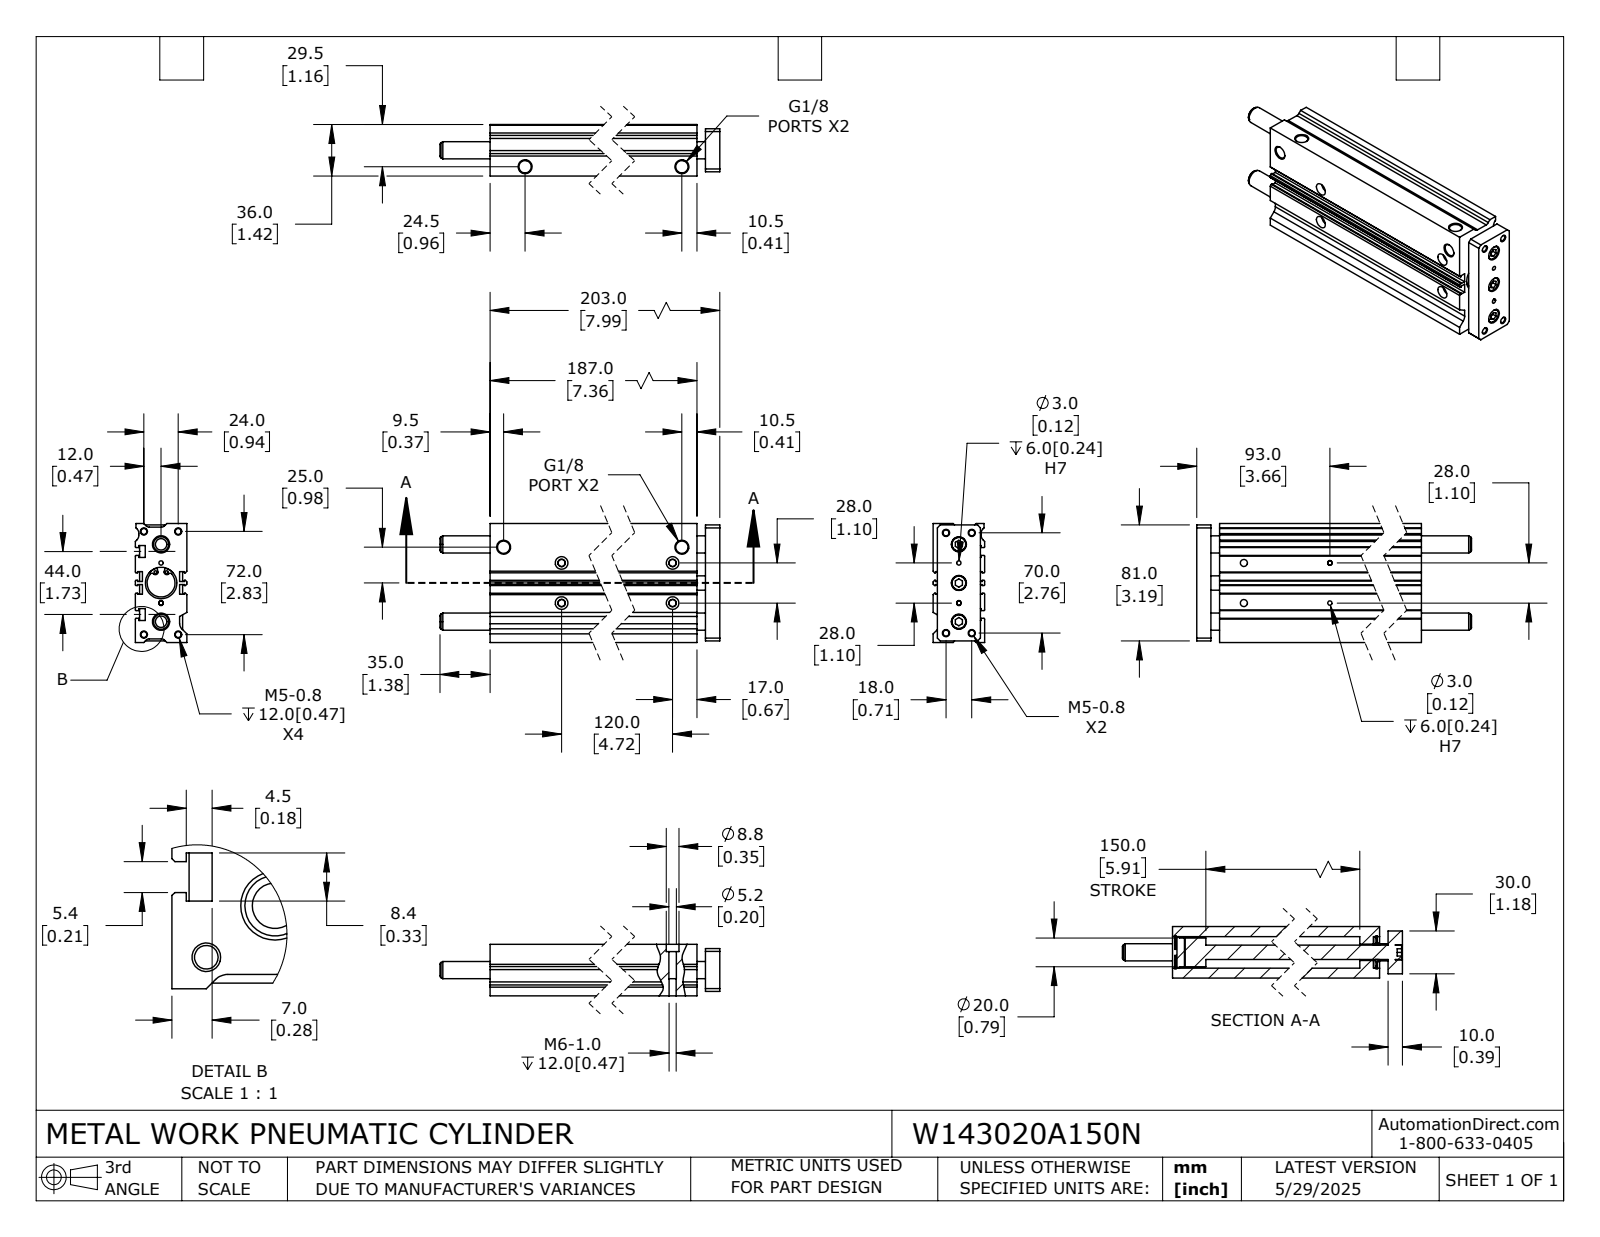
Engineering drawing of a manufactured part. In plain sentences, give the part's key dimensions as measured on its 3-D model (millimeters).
The part is named "W143020A150N_ROD; W143020A150N; W143020A150N_BODY". Its 3-D file was written by "SolidWorks 2024 (CONFIG_CONTROL_DESIGN)". It is 6 solids with 357 faces: 174 planar, 145 cylindrical and 38 other. Overall it measures 238 by 83 by 36 millimeters. Its volume is 467 500 cubic millimeters and its surface area 133 000 square millimeters. Round holes: 8 of diameter 4.1, 4 of diameter 2, 4 of diameter 3, 4 of diameter 5.2, 4 of diameter 8.6, 4 of diameter 8.8, 3 of diameter 10.5, 2 of diameter 4.9, 2 of diameter 4.9, 2 of diameter 12, 1 of diameter 11.4, 1 of diameter 19.5. Round bosses or shafts: 3 of diameter 10, 2 of diameter 23, 1 of diameter 20, 1 of diameter 13. Partial cylindrical surfaces (rounded edges, fillets, slot ends): 4 of radius 1.3, 4 of radius 1.5, 4 of radius 1.8, 4 of radius 3, 3 of radius 5. The main face-to-face distances are 36, 2.5, 5, 31, 2, 83, 26, 7, 80.5, 24. The hole center spacings are 3.1, 7.5, 8.5, 12, 15, 19.8, 21, 21.9.
